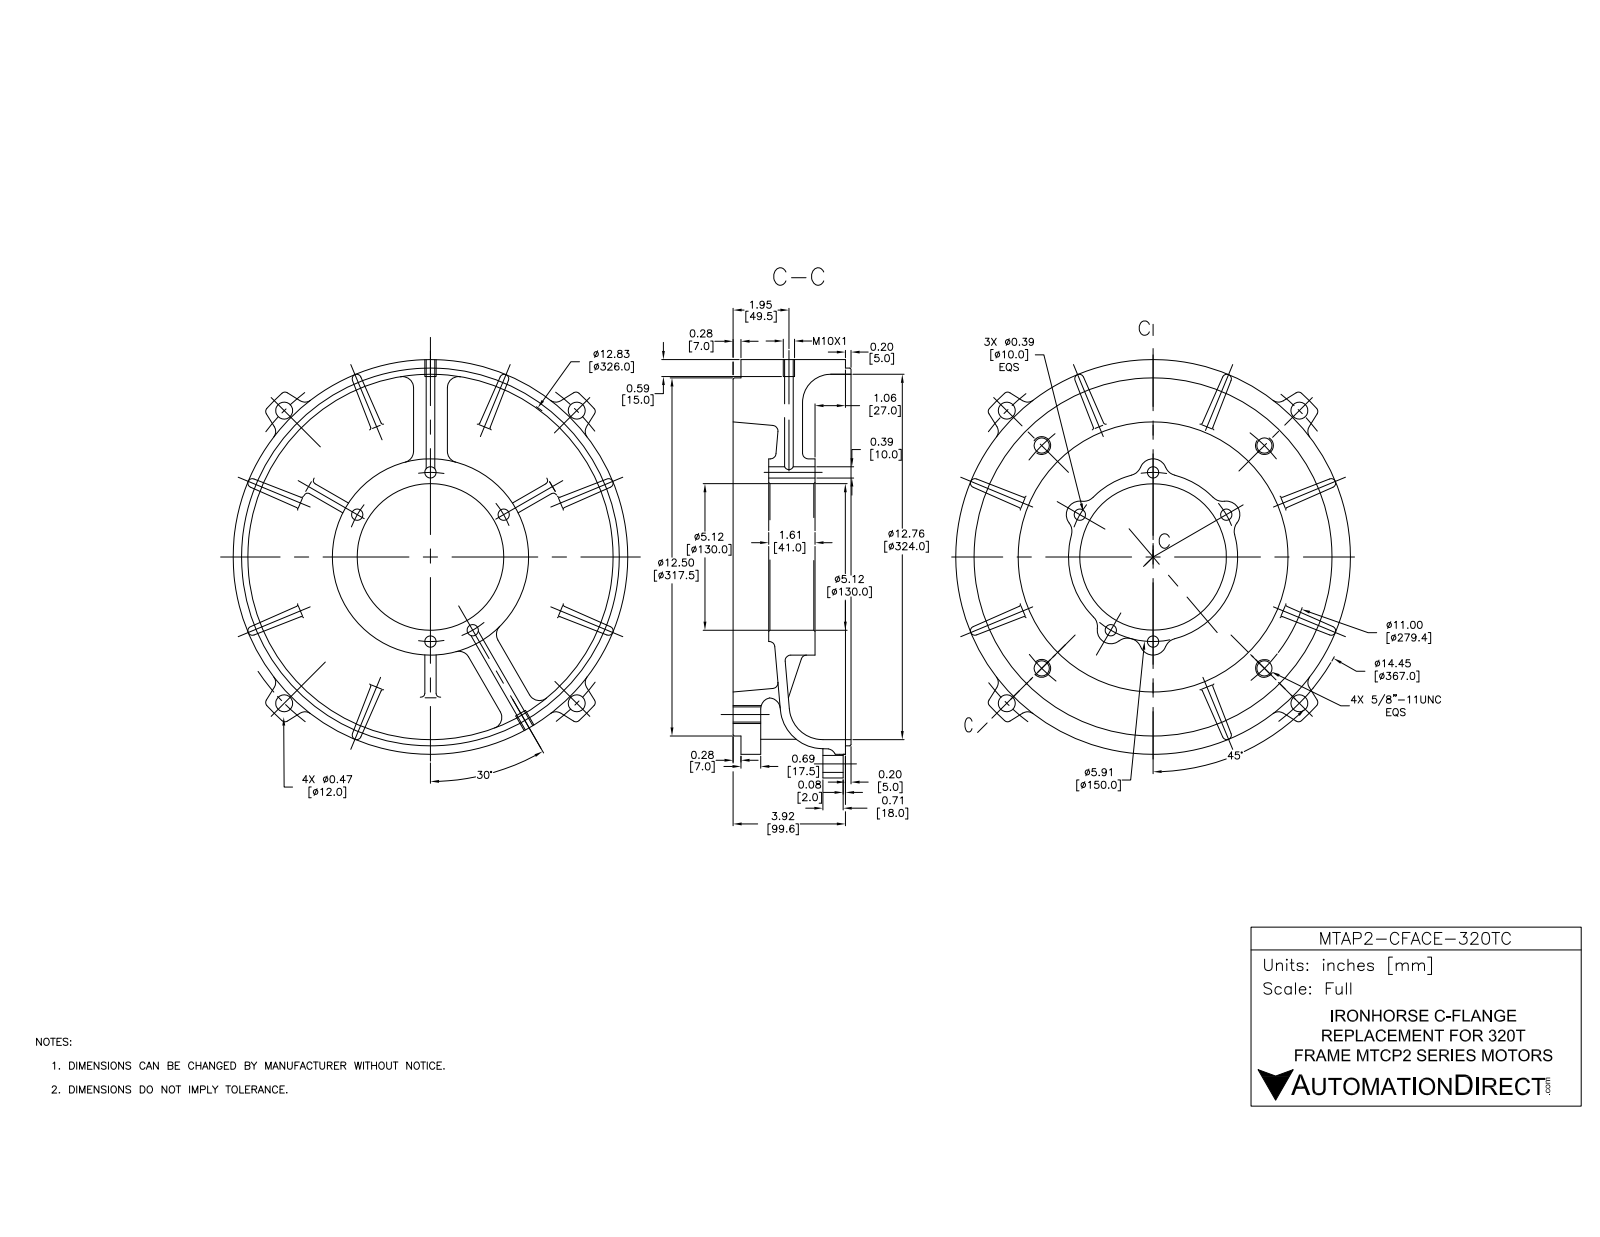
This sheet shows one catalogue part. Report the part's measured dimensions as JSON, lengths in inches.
{"part_name": "MTAP2-CFACE-320TC", "step_written_by": "SolidWorks 2017 (AUTOMOTIVE_DESIGN)", "units": "inches", "bodies": {"solids": 10, "faces": 475, "planar": 86, "cylindrical": 179, "other": 210}, "overall_size": [13.78, 13.78, 4.118], "volume_in3": 205, "surface_area_in2": 1043, "round_holes": [[0.394, 7], [0.551, 4], [0.591, 4], [0.315, 2], [2.362, 1], [3.346, 1], [4.717, 1], [5.118, 1], [12.756, 1]], "round_bosses_or_shafts": [[13.78, 1], [13.189, 1], [12.5, 1], [5.11, 1]], "partial_cylinders_radius": [[0.472, 19], [0.164, 14], [0.157, 8], [0.315, 8], [0.197, 3], [0.354, 2], [1.87, 1], [2.953, 1]], "face_to_face_distances": [0.965, 0.276, 0.969, 1.244, 0.28, 0.689, 2.858, 2.677, 3.921, 3.646], "hole_center_spacings": [2.953, 3.527, 4, 4.355, 5.5, 6.998, 7.778, 7.87]}
